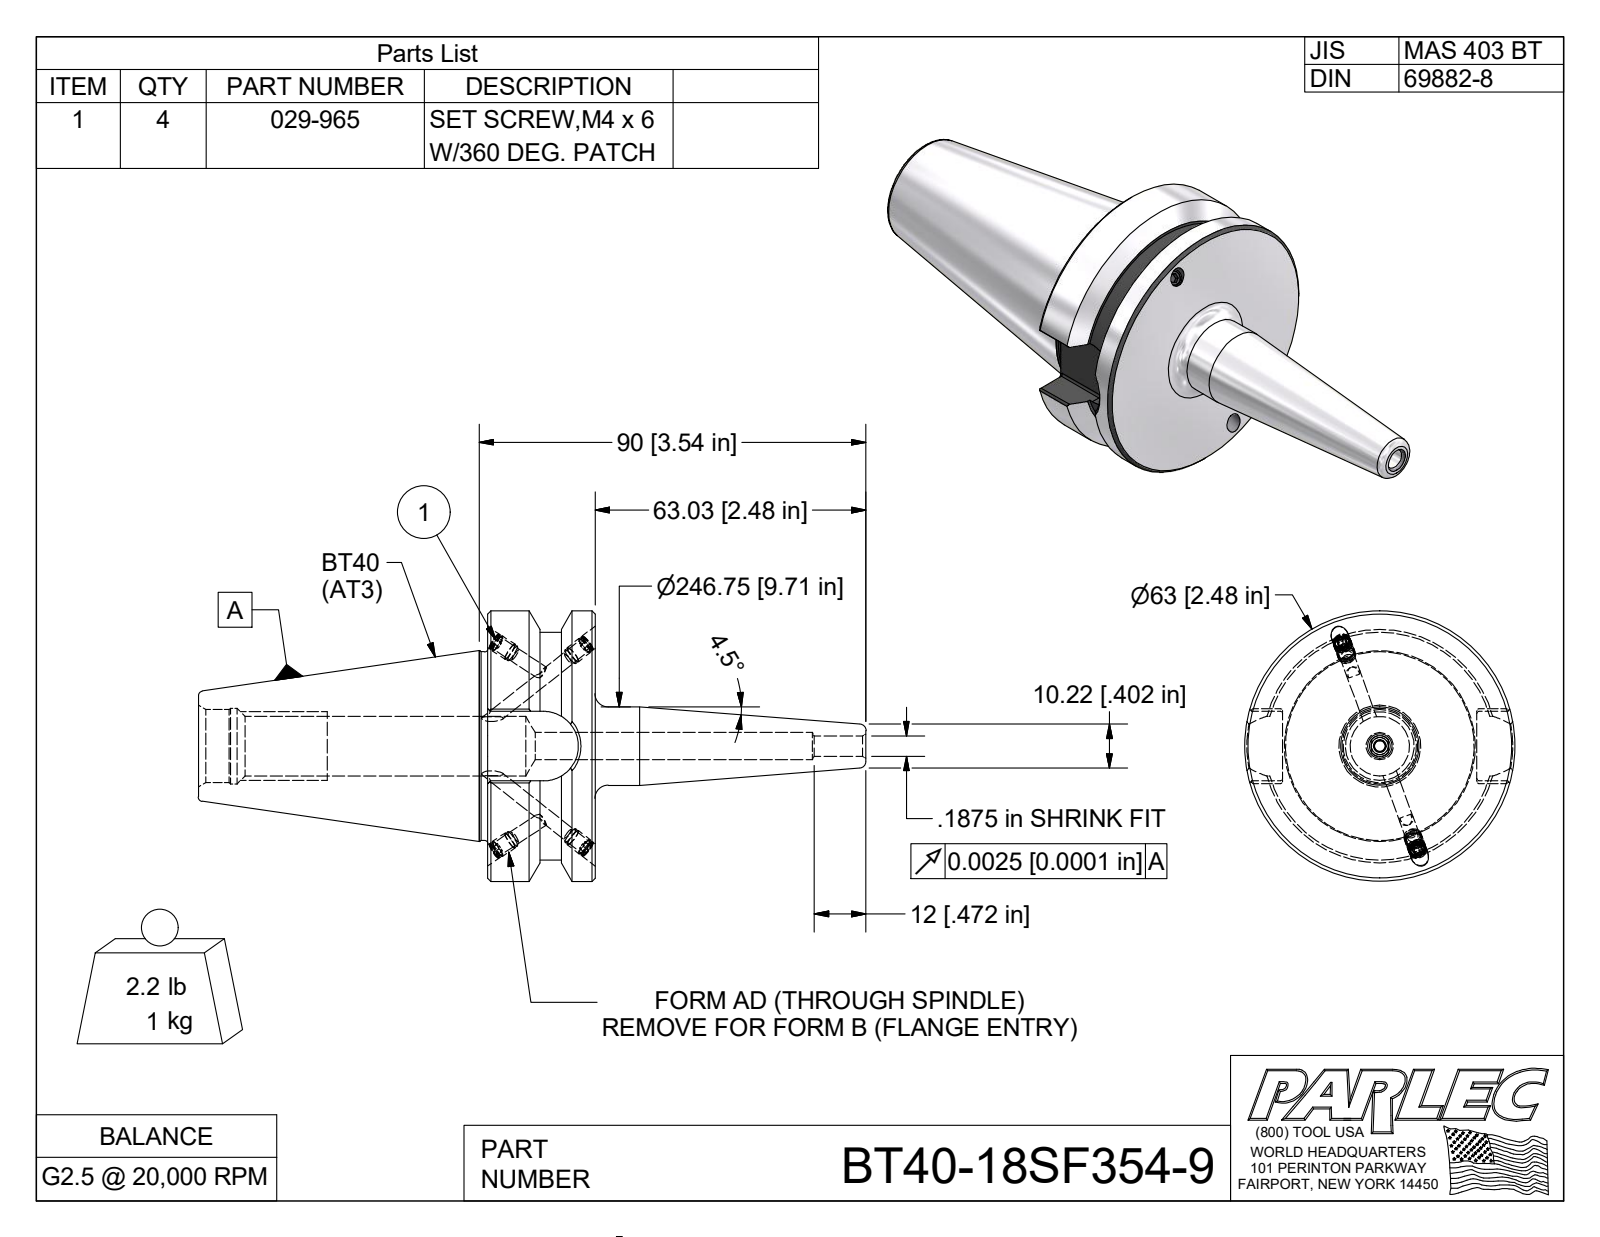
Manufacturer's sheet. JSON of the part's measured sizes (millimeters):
{"part_name": "BT40-18SF354-9; BT40BC-18SF354-9-1; 029-965; BS-SFM058-16", "step_written_by": "Autodesk Inventor 2009 (AUTOMOTIVE_DESIGN)", "units": "millimeters", "bodies": {"solids": 6, "faces": 170, "planar": 78, "cylindrical": 42, "other": 50}, "overall_size": [155.4, 63, 63], "volume_mm3": 130300, "surface_area_mm2": 27720, "round_holes": [[3.3, 4], [4.1, 4], [4.7, 1], [17.6, 1]], "round_bosses_or_shafts": [[4.2, 4], [4, 4], [63, 1], [53, 1], [44.5, 1], [43.9, 1], [18.3, 1]], "partial_cylinders_radius": [[0.5, 8], [2.5, 1], [8.1, 1]], "face_to_face_distances": [25, 45.2, 67.4, 92.4, 16.2, 20.6, 24.6, 84.5, 17.1, 7.8]}
